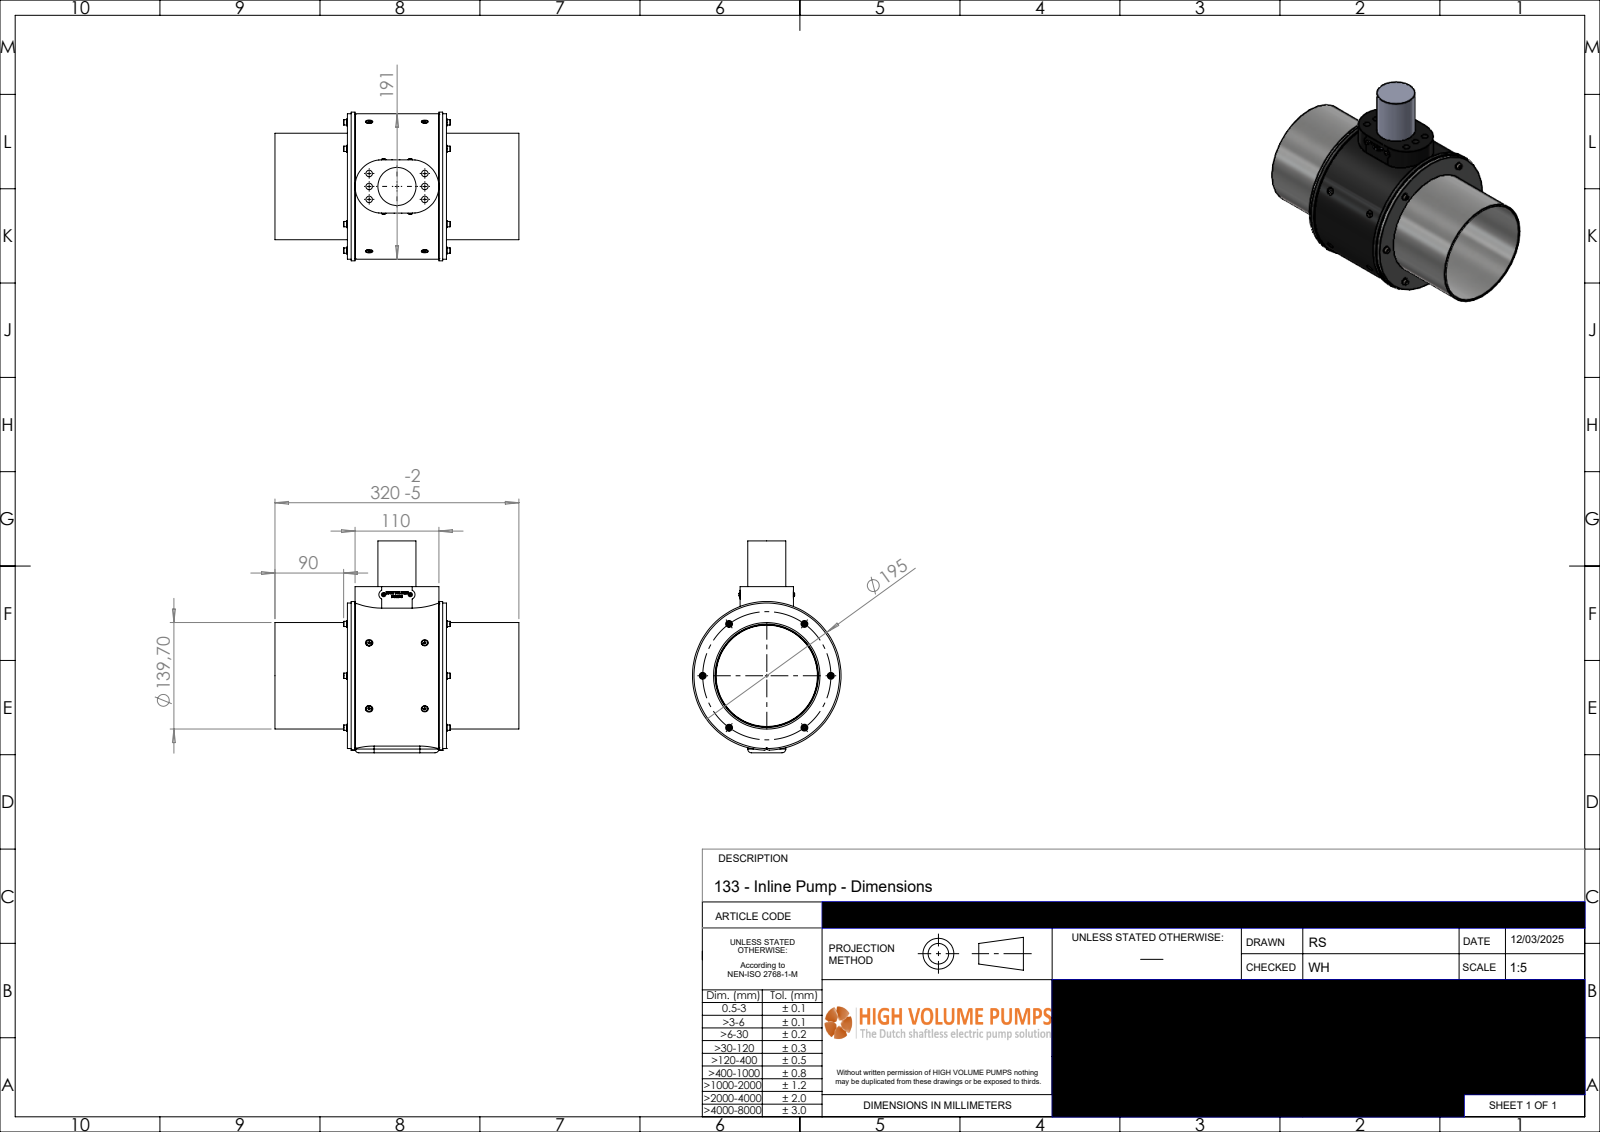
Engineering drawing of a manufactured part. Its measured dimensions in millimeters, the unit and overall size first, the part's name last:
Units: millimetres
Overall size (bounding box): 320.06 × 278 × 195
Round holes (diameter × count): ⌀4.6 ×6, ⌀8.5 ×6, ⌀133 ×1, ⌀135.7 ×1
Round bosses / shafts (diameter × count): ⌀9 ×6, ⌀7 ×6, ⌀4 ×6, ⌀9.64 ×5, ⌀7.64 ×4, ⌀5.7 ×2, ⌀195 ×1, ⌀191 ×1
Partial cylindrical surfaces — rounded edges, fillets, slot ends (radius × count): R5 ×6, R3.82 ×4, R1 ×2, R2 ×2, R2.25 ×2, R6.25 ×2, R20 ×2, R25 ×2
Main face-to-face distances: 130.06, 5, 120.06, 10, 218, 125.06, 115.06, 60, 95, 278
Hole centre spacings: 84.1, 17, 74.95, 76.36, 149.87, 73, 168.2, 34
Volume: 2 325 000 mm³ · Surface area: 357 816 mm²
Bodies: 1 solid, 969 faces (636 planar, 142 cylindrical, 191 other)
Part name (STEP PRODUCT): P-133-030-rev-B-IP
STEP written by: SolidWorks 2024 (AUTOMOTIVE_DESIGN)
